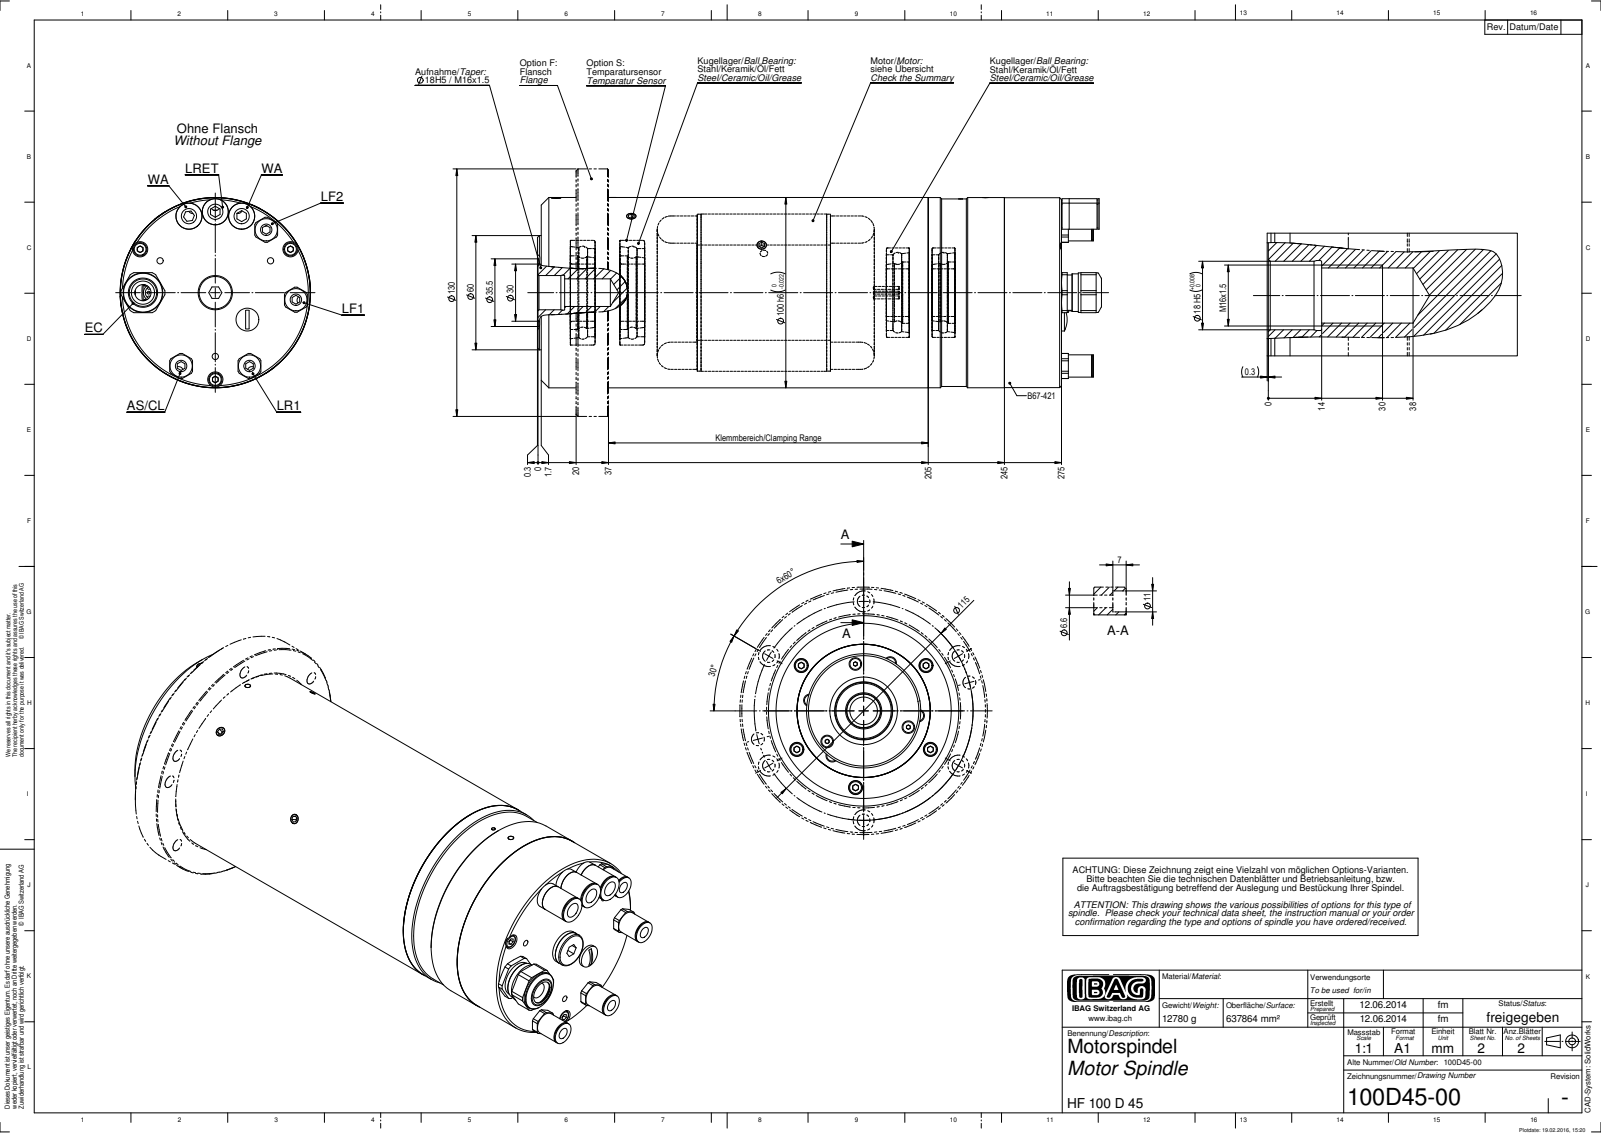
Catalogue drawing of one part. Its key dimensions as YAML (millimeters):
part_name: "100D45-00"
step_written_by: "SolidWorks 2014 (CONFIG_CONTROL_DESIGN)"
units: millimeters
bodies: {solids: 0, faces: 546, planar: 234, cylindrical: 203, other: 109}
overall_size: [296.3, 100.05, 100]
round_holes:
  - {diameter: 6, count: 5}
  - {diameter: 7.4, count: 5}
  - {diameter: 8, count: 5}
  - {diameter: 3.3, count: 3}
  - {diameter: 5, count: 1}
  - {diameter: 8.5, count: 1}
  - {diameter: 12.2, count: 1}
  - {diameter: 18.4, count: 1}
  - {diameter: 19.15, count: 1}
  - {diameter: 30.5, count: 1}
  - {diameter: 35.5, count: 1}
  - {diameter: 70, count: 1}
round_bosses_or_shafts:
  - {diameter: 5.7, count: 7}
  - {diameter: 11.7, count: 5}
  - {diameter: 10.53, count: 3}
  - {diameter: 13.7, count: 2}
  - {diameter: 13.7, count: 2}
  - {diameter: 7, count: 2}
  - {diameter: 100, count: 1}
  - {diameter: 99.9, count: 1}
partial_cylinders:
  - {radius: 6.6, count: 5}
  - {radius: 11.55, count: 1}
face_to_face_distances: [273.3, 203.3, 70, 243.3, 40, 30, 18.3, 185, 225, 255]
hole_center_spacings: [42.5, 68.77, 25.03, 37.49, 56.09, 6.8, 12.1, 33.5]
